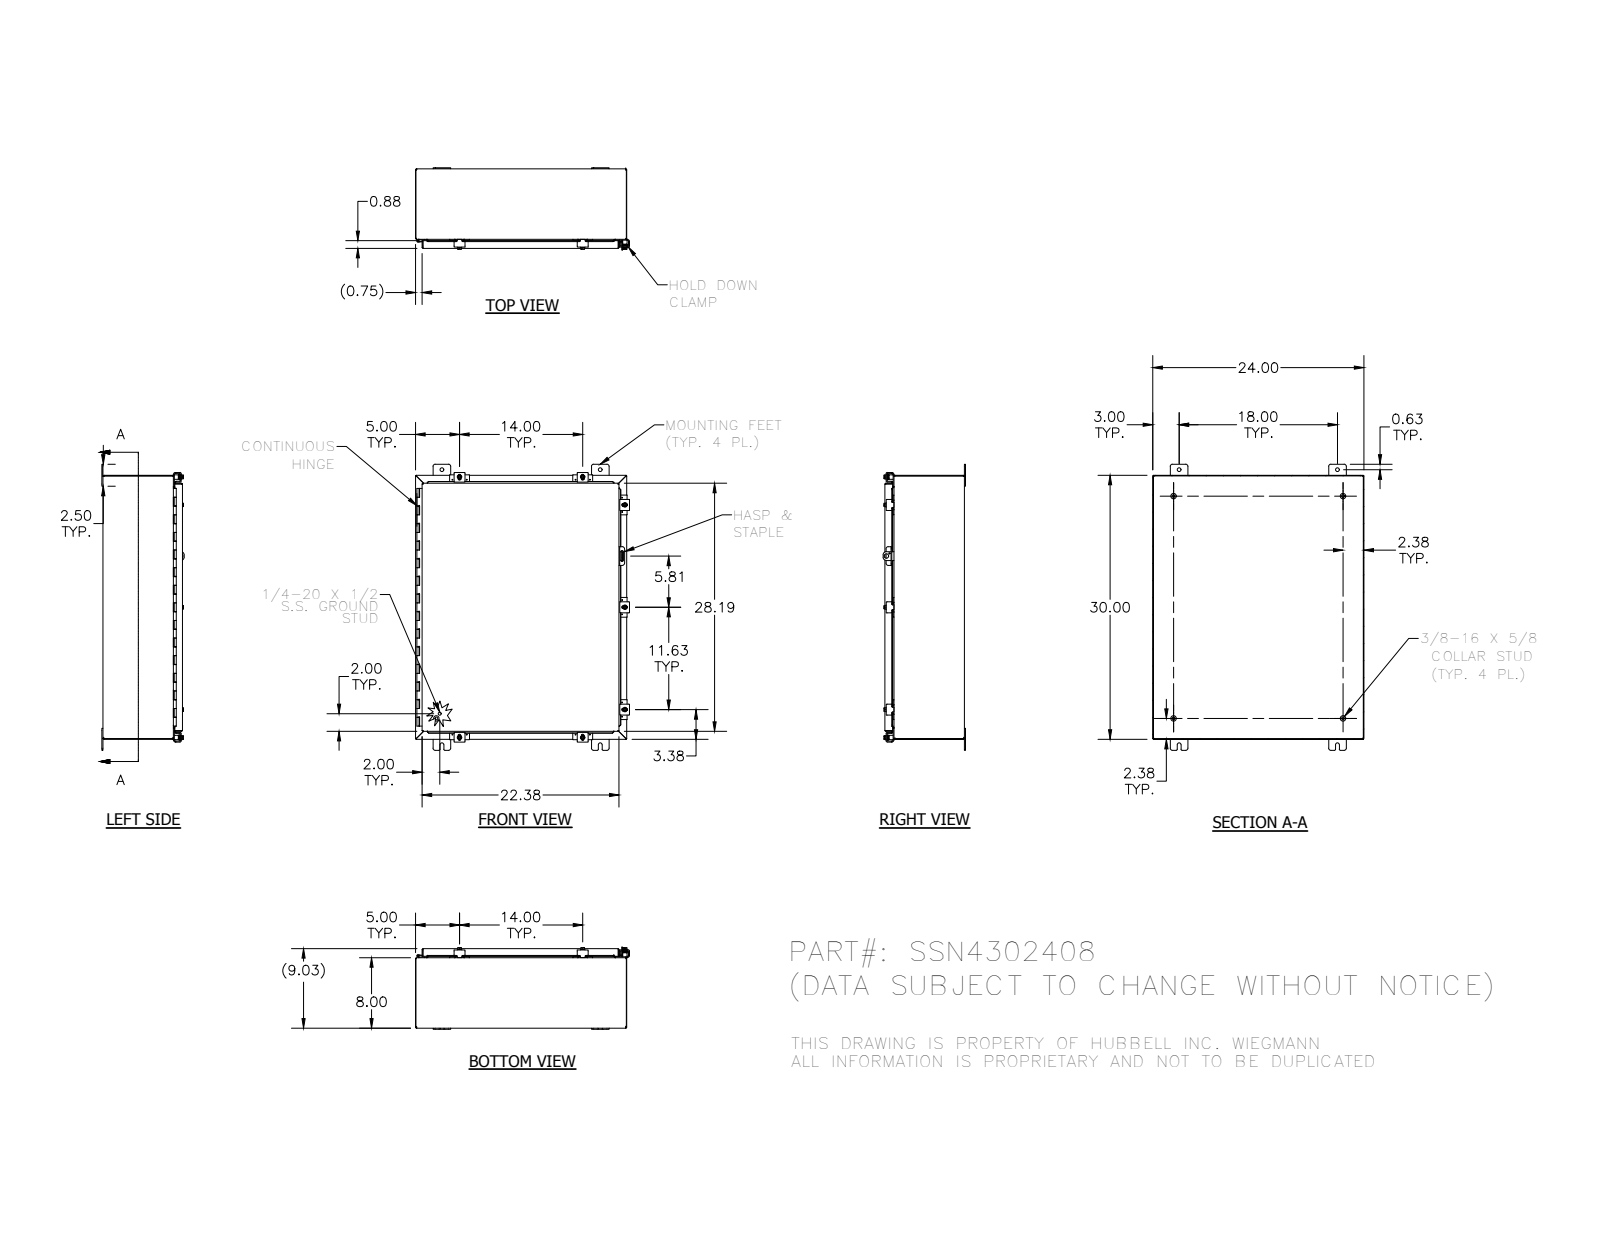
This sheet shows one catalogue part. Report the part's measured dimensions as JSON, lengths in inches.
{"part_name": "SSN43024LID; 38846; 30818; 28x22 (+8 more)", "step_written_by": "SolidWorks 2014 (AUTOMOTIVE_DESIGN)", "units": "inches", "bodies": {"solids": 52, "faces": 2111, "planar": 805, "cylindrical": 935, "other": 371}, "overall_size": [32.5, 24.311, 9.355], "volume_in3": 208.1, "surface_area_in2": 5471, "round_holes": [[0.11, 14], [0.211, 7], [0.281, 7], [0.3, 7], [0.438, 4], [0.125, 1], [0.156, 1], [0.5, 1]], "round_bosses_or_shafts": [[0.25, 9], [0.52, 7], [0.5, 7], [0.35, 7], [0.625, 4], [0.33, 4], [0.115, 2], [0.337, 1]], "partial_cylinders_radius": [[0.03, 83], [0.125, 37], [0.25, 33], [0.031, 23], [0.105, 23], [0.062, 15], [0.141, 14], [0.1, 10]], "face_to_face_distances": [0.074, 8.959, 8.885, 9.033, 23.926, 29.926, 7.926, 1.033, 23.852, 24], "hole_center_spacings": [0.876, 29.3, 14, 1.625, 13.191, 14.816, 28.961, 29.006]}
